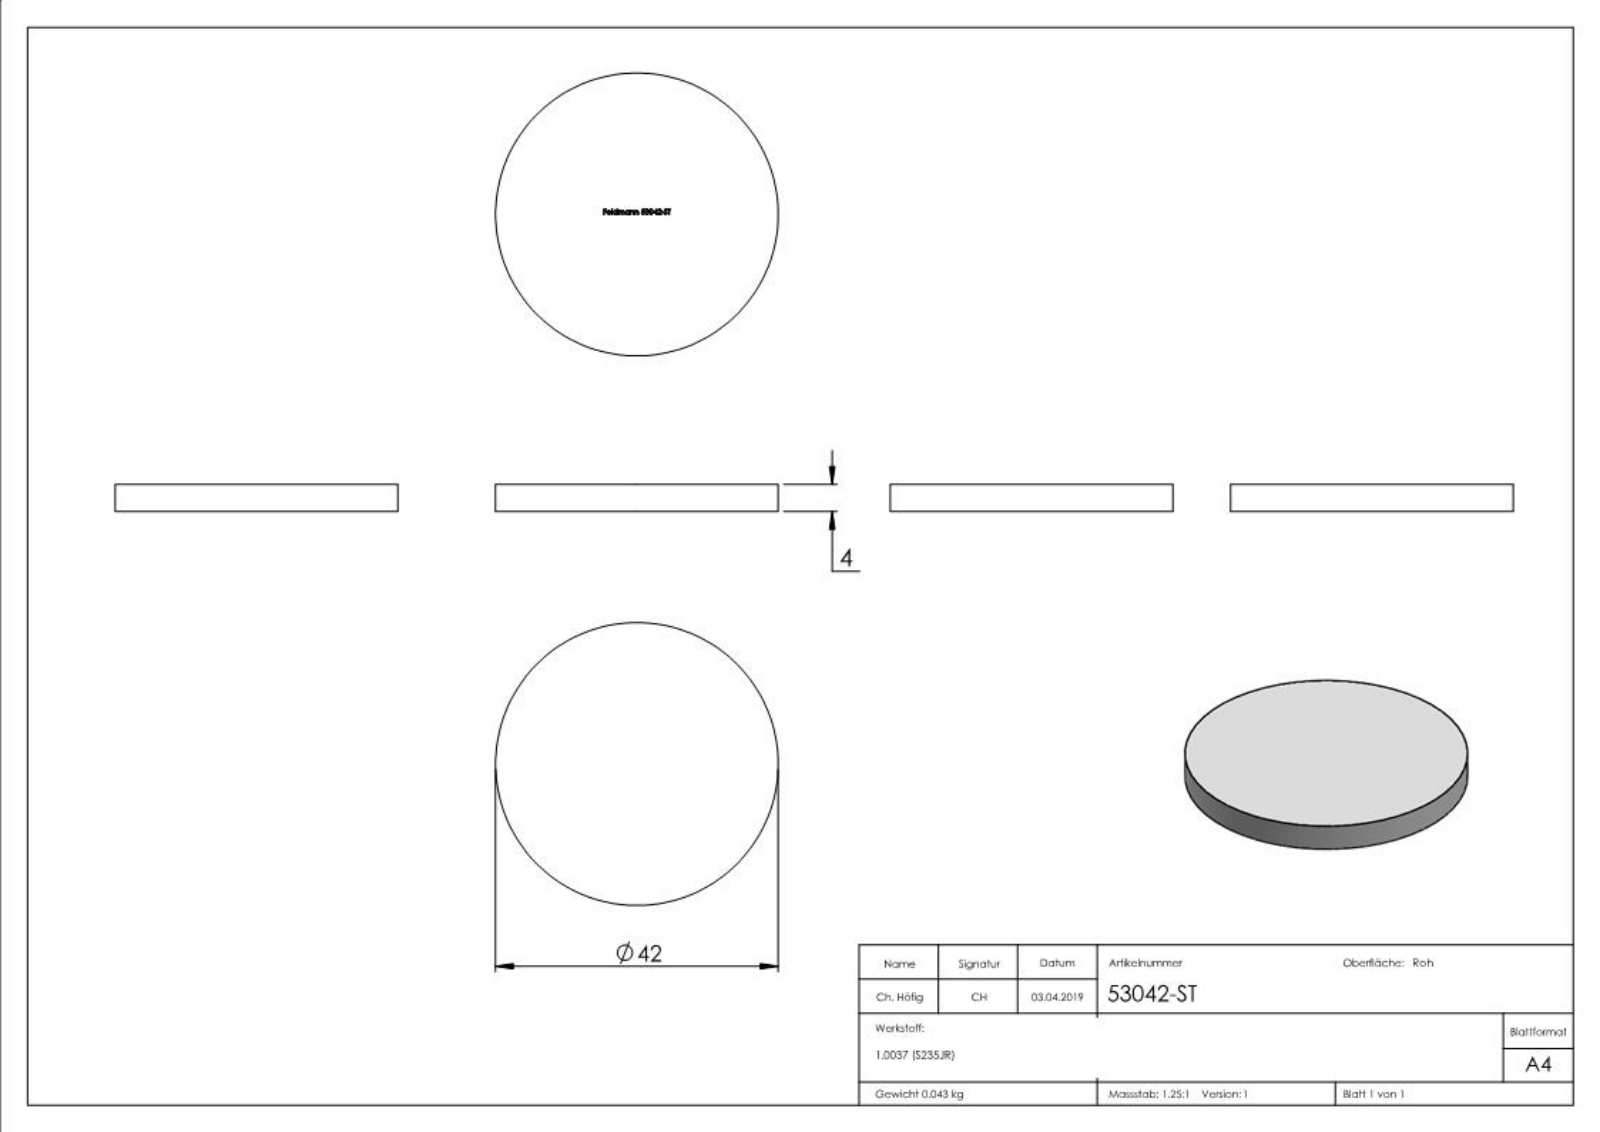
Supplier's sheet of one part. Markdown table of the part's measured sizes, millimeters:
| quantity | value |
| --- | --- |
| part name | 53042-ST |
| STEP written by | SolidWorks 2015 (CONFIG_CONTROL_DESIGN) |
| units | millimeters |
| bodies | 1 solid, 221 faces (119 planar, 2 cylindrical, 100 other) |
| overall size | 42 × 42 × 4 |
| volume | 5 542 mm³ |
| surface area | 3 304 mm² |
| round bosses / shafts (diameter × count) | 42 × 1 |
| main face-to-face distances | 4, 3.9, 0.79, 0.44, 0.99, 1.78, 1.21, 8.49, 9.7, 0.71 |
